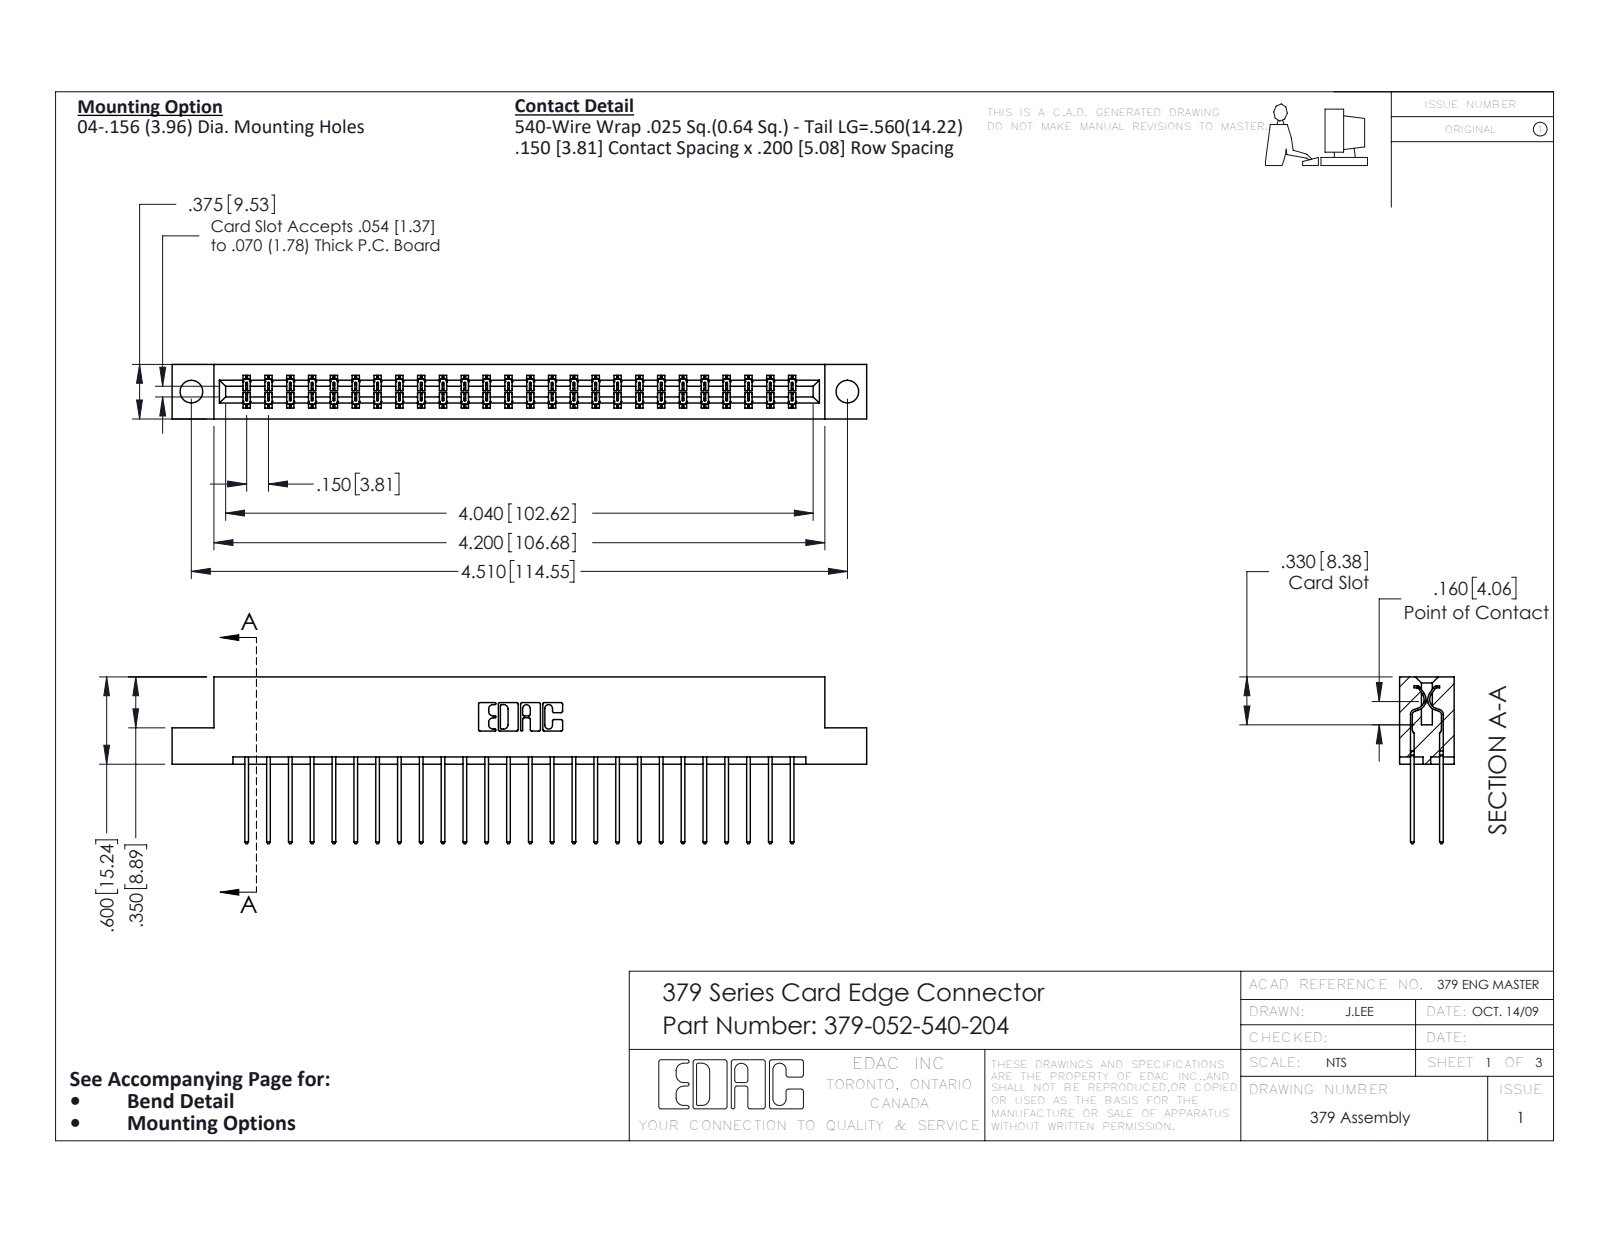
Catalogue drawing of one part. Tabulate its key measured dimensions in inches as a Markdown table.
| quantity | value |
| --- | --- |
| part name | 379 Part_Flush - .156 Dia - TH; 379-052-540-204; 345-292-001_345-293-140 |
| STEP written by | SolidWorks 2016 (CONFIG_CONTROL_DESIGN) |
| units | inches |
| bodies | 53 solids, 2818 faces (1942 planar, 876 cylindrical, 0 other) |
| overall size | 4.775 × 1.147 × 0.375 |
| volume | 0.783 in³ |
| surface area | 23.31 in² |
| round holes (diameter × count) | 0.156 × 2 |
| partial cylindrical surfaces (radius × count) | 0.006 × 78, 0.01 × 52, 0.01 × 22, 0.007 × 6, 0.031 × 6, 0.026 × 3, 0.014 × 2, 0.022 × 2 |
| main face-to-face distances | 0.3, 0.075, 0.375, 0.2, 0.1, 0.275, 0.025, 0.15, 0.076, 0.225 |
| hole center spacings | 4.51 |
